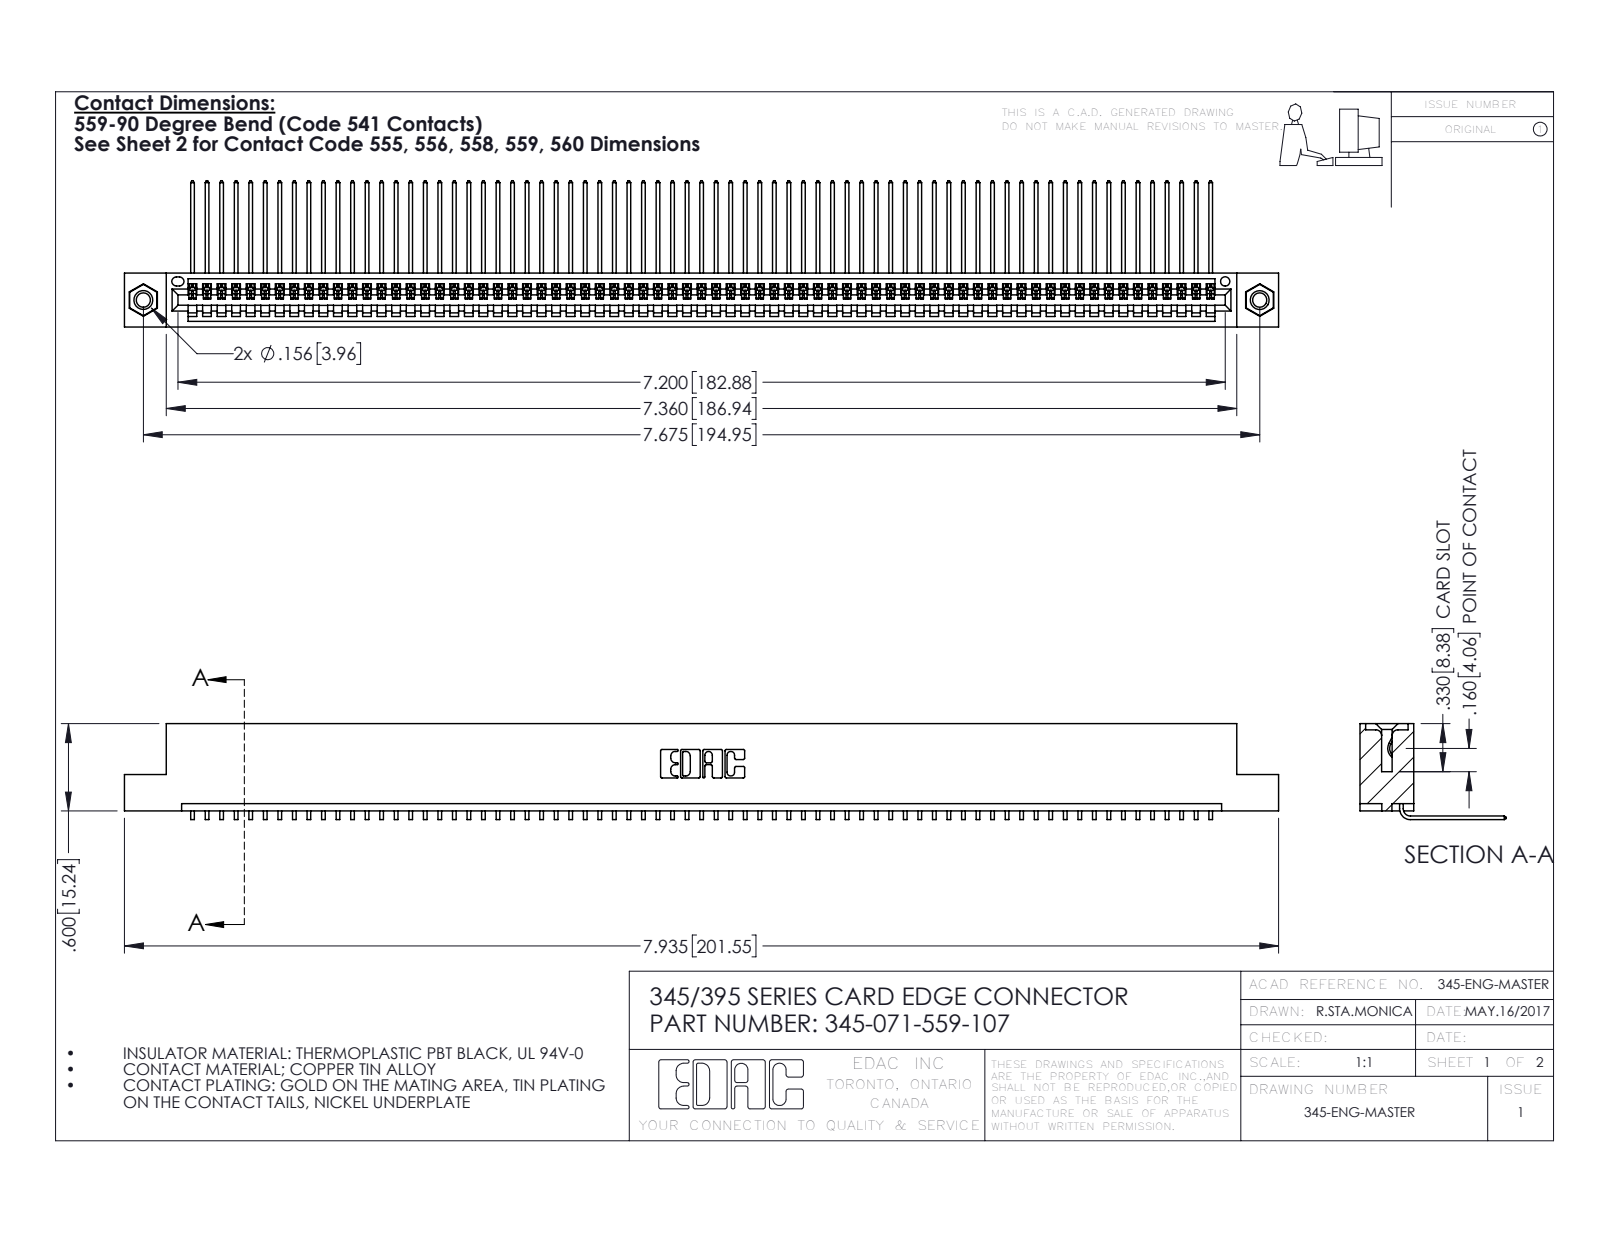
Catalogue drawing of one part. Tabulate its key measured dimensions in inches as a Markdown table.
| quantity | value |
| --- | --- |
| part name | 345-250-001_345-250-005-103; 345 Part_Flush Mounting Lugs - 0.156 Dia-TI; 345-071-559-107; 345-292-001_558 559 Tail - 1 |
| STEP written by | SolidWorks 2016 (CONFIG_CONTROL_DESIGN) |
| units | inches |
| bodies | 74 solids, 4446 faces (3094 planar, 1336 cylindrical, 16 other) |
| overall size | 7.935 × 1.005 × 0.659 |
| volume | 1.196 in³ |
| surface area | 43.2 in² |
| round holes (diameter × count) | 0.098 × 2, 0.125 × 2, 0.156 × 2, 0.064 × 1 |
| round bosses / shafts (diameter × count) | 0.155 × 2 |
| partial cylindrical surfaces (radius × count) | 0.006 × 142, 0.01 × 22, 0.007 × 6, 0.031 × 6, 0.026 × 3, 0.031 × 2, 0.04 × 2, 0.014 × 1 |
| main face-to-face distances | 0.072, 0.298, 0.37, 0.2, 0.098, 0.272, 0.025, 0.225, 0.149, 0.072 |
| hole center spacings | 0.27, 7.439, 7.675 |
